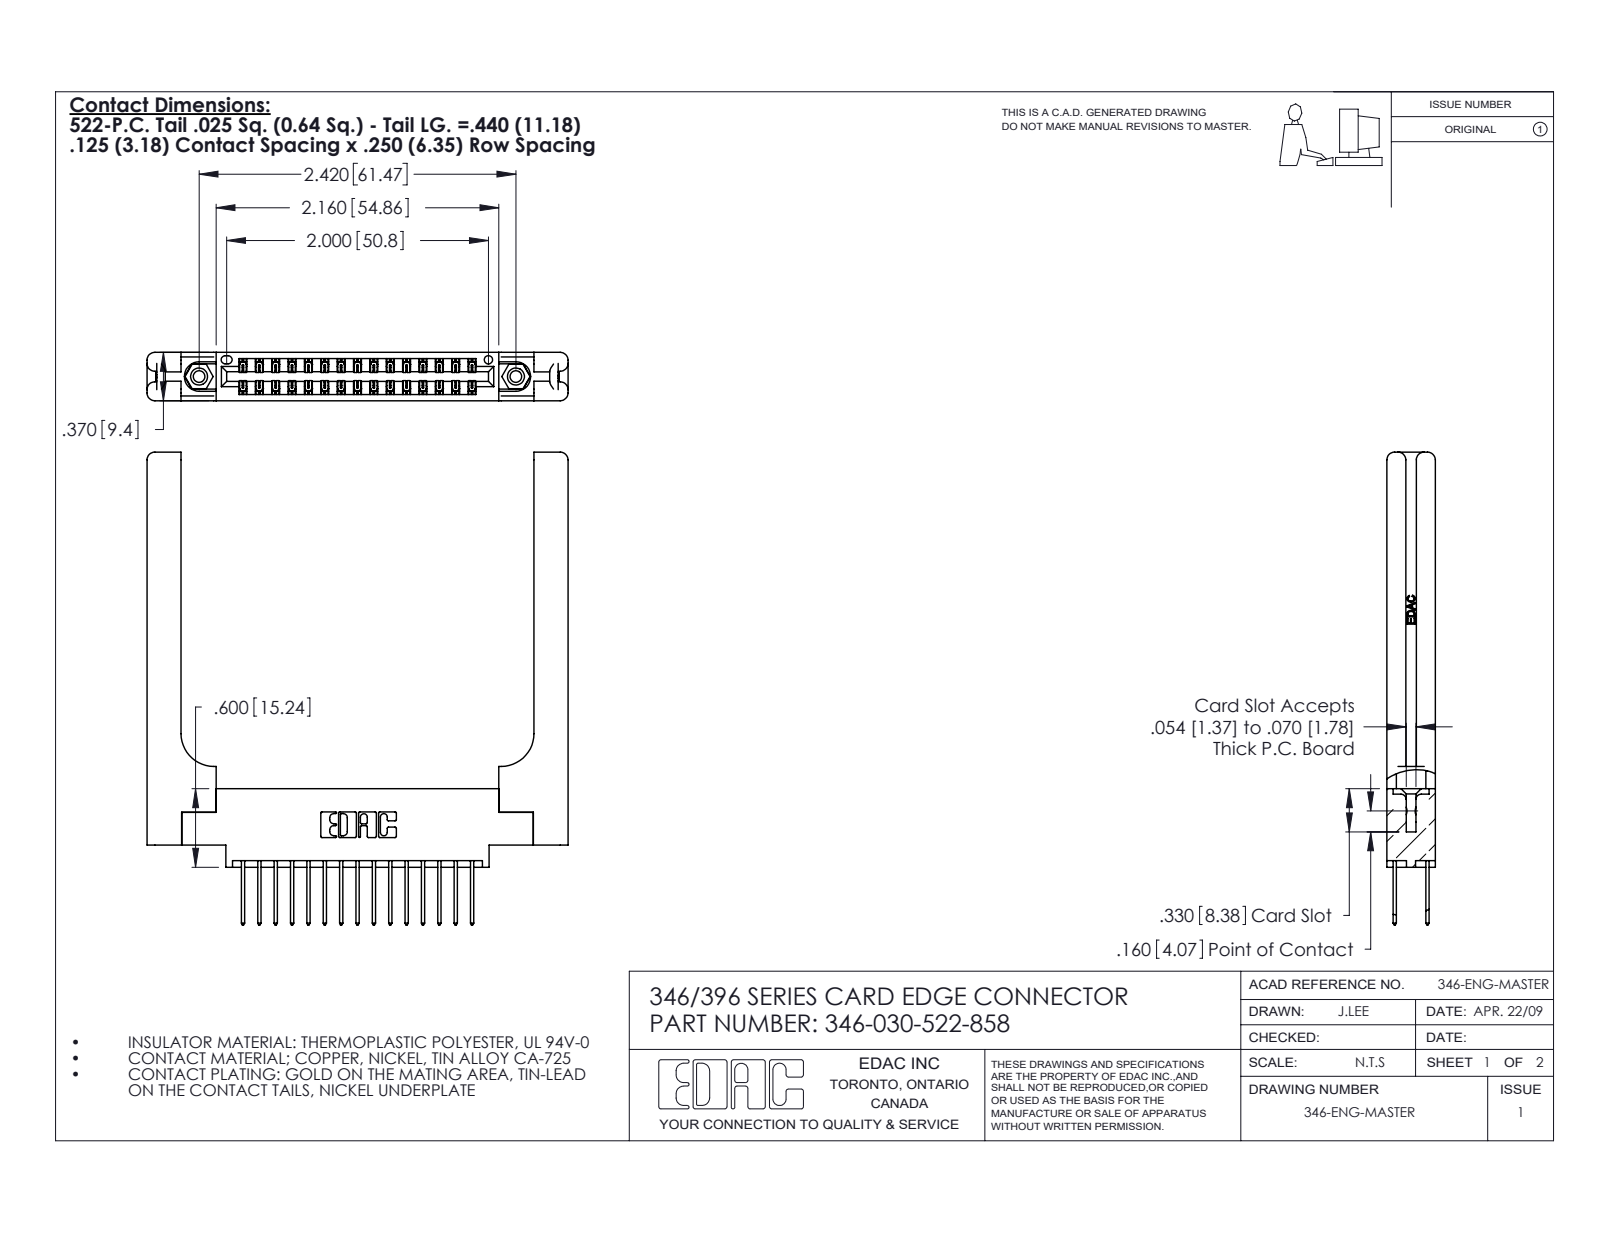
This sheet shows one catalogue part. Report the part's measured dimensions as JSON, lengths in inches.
{"part_name": "346 Part_0.170 Offset - 0.156 Dia-TH; 346-220-058_345-220-058; 345-250-001_345-250-001-102; 345-292-001_345-293-122 (+1 more)", "step_written_by": "SolidWorks 2020 (CONFIG_CONTROL_DESIGN)", "units": "inches", "bodies": {"solids": 35, "faces": 1956, "planar": 1292, "cylindrical": 604, "other": 60}, "overall_size": [3.61, 3.216, 0.37], "volume_in3": 0.925, "surface_area_in2": 24.25, "round_holes": [[0.089, 2], [0.125, 2], [0.156, 2], [0.064, 1]], "round_bosses_or_shafts": [[0.155, 2]], "partial_cylinders_radius": [[0.006, 45], [0.01, 30], [0.01, 22], [0.06, 16], [0.007, 6], [0.031, 6], [0.026, 3], [0.014, 2]], "face_to_face_distances": [0.37, 0.072, 0.048, 0.322, 0.148, 0.15, 0.25, 0.025, 0.298, 0.077], "hole_center_spacings": [0.246, 2.213, 2.42]}
